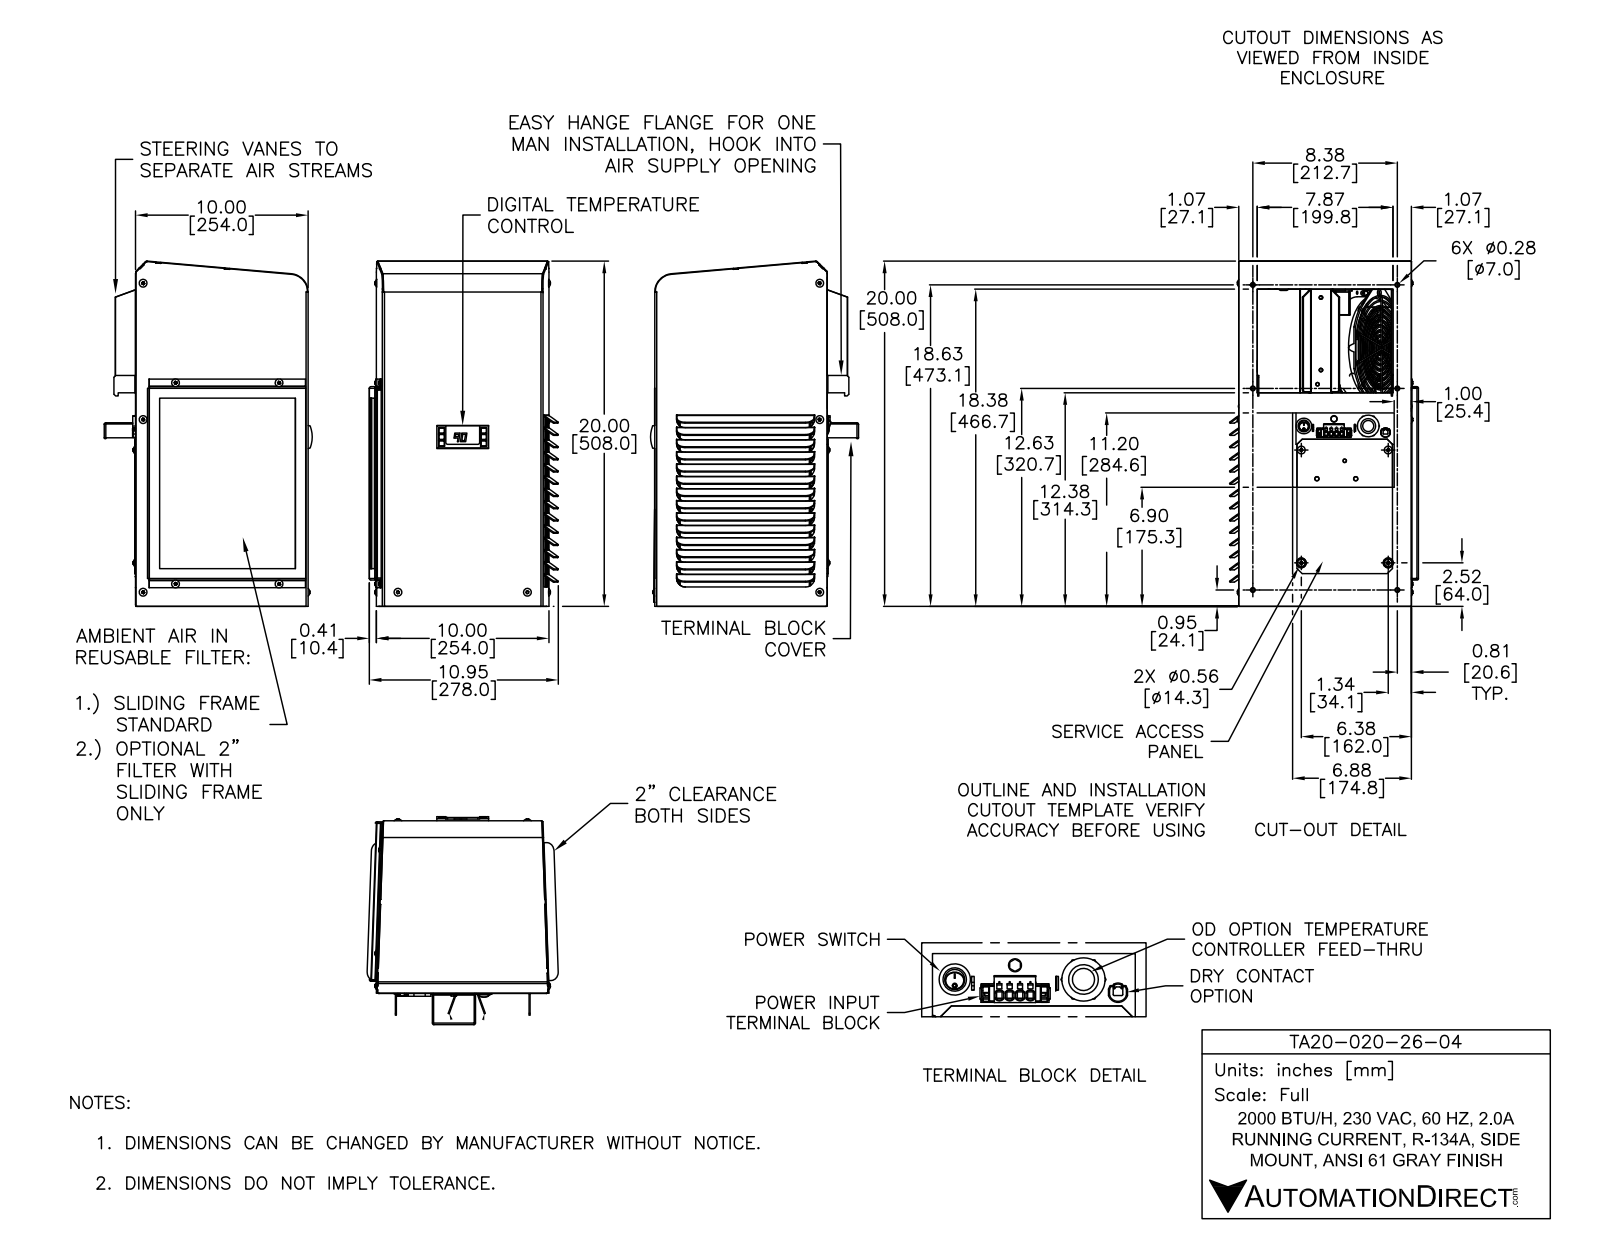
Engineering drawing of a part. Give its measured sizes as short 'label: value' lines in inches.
name: TA20-020-26-04
written by: SolidWorks 2019 (AUTOMOTIVE_DESIGN)
unit: in
bodies: 52 solids, 2157 faces (1121 planar, 737 cylindrical, 299 other)
size: 20 × 11.344 × 11.002
volume: 401.3 in³; area: 2 755 in²
holes: 17× ⌀0.204, 6× ⌀0.2, 6× ⌀0.344, 4× ⌀0.045, 4× ⌀0.12, 4× ⌀0.14, 4× ⌀0.166, 4× ⌀0.219, 2× ⌀0.091, 2× ⌀0.126, 2× ⌀0.166, 2× ⌀0.25
bosses: 16× ⌀0.19, 6× ⌀0.44, 2× ⌀0.36, 2× ⌀0.106, 1× ⌀1, 1× ⌀0.906, 1× ⌀0.865, 1× ⌀0.832
rounds: 100× R0.015, 96× R0.01, 44× R0.031, 33× R0.03, 22× R0.1, 16× R0.011, 14× R0.091, 13× R0.089
face distances: 0.06, 0.058, 10, 9.94, 9.942, 9.882, 0.185, 0.244, 2.624, 2.809
hole spacings: 0.2, 0.4, 6, 6, 11.65, 13.104, 8.251, 8.375
